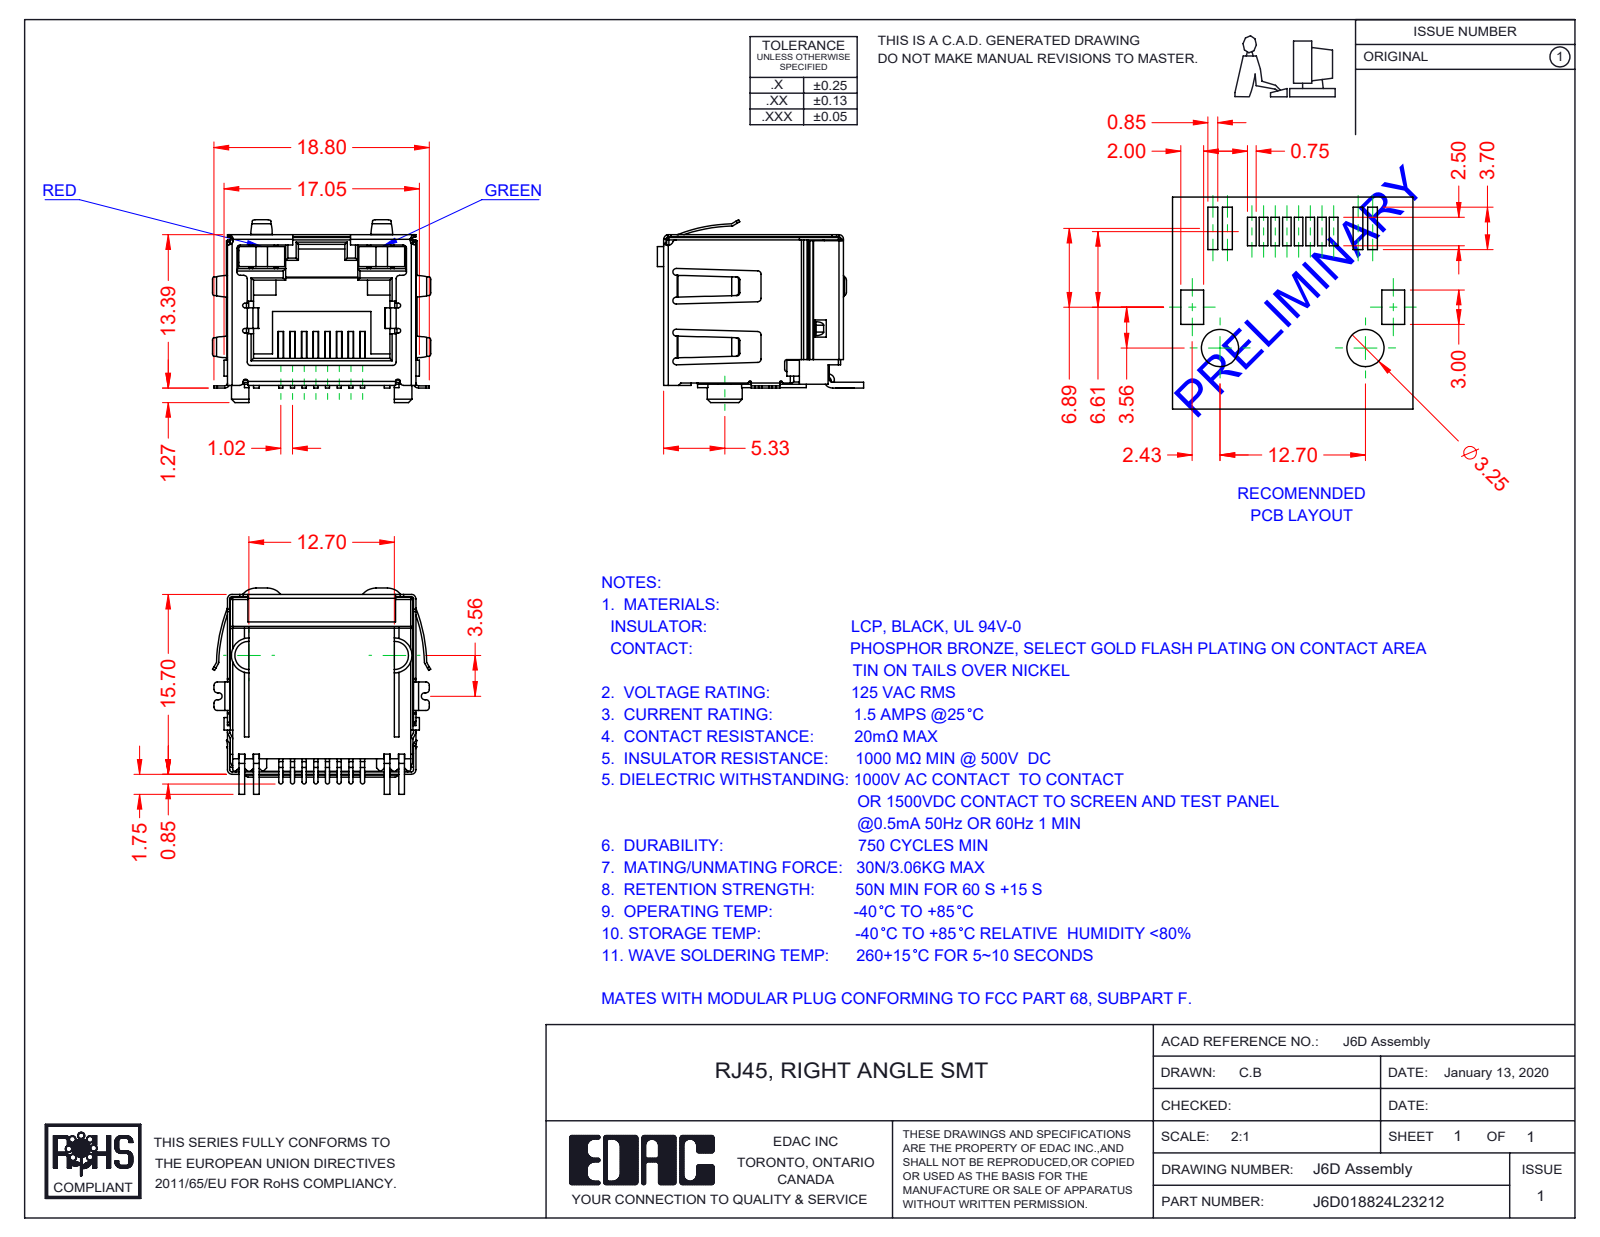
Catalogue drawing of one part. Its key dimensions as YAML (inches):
part_name: "6D Contacts; 6D LED RH_3-Green; 6D LED LH_2-Red; J6D018824L23212 (+2 more)"
step_written_by: "SolidWorks 2016 (CONFIG_CONTROL_DESIGN)"
units: inches
bodies: {solids: 12, faces: 1028, planar: 701, cylindrical: 282, other: 45}
overall_size: [0.75, 0.709, 0.628]
volume: 0.109
surface_area: 7.434
partial_cylinders:
  - {radius: 0.012, count: 55}
  - {radius: 0.008, count: 40}
  - {radius: 0.016, count: 19}
  - {radius: 0.01, count: 16}
  - {radius: 0.004, count: 12}
  - {radius: 0.006, count: 8}
  - {radius: 0.007, count: 8}
  - {radius: 0.02, count: 6}
face_to_face_distances: [0.63, 0.638, 0.64, 0.089, 0.039, 0.628, 0.504, 0.018, 0.514, 0.417]
